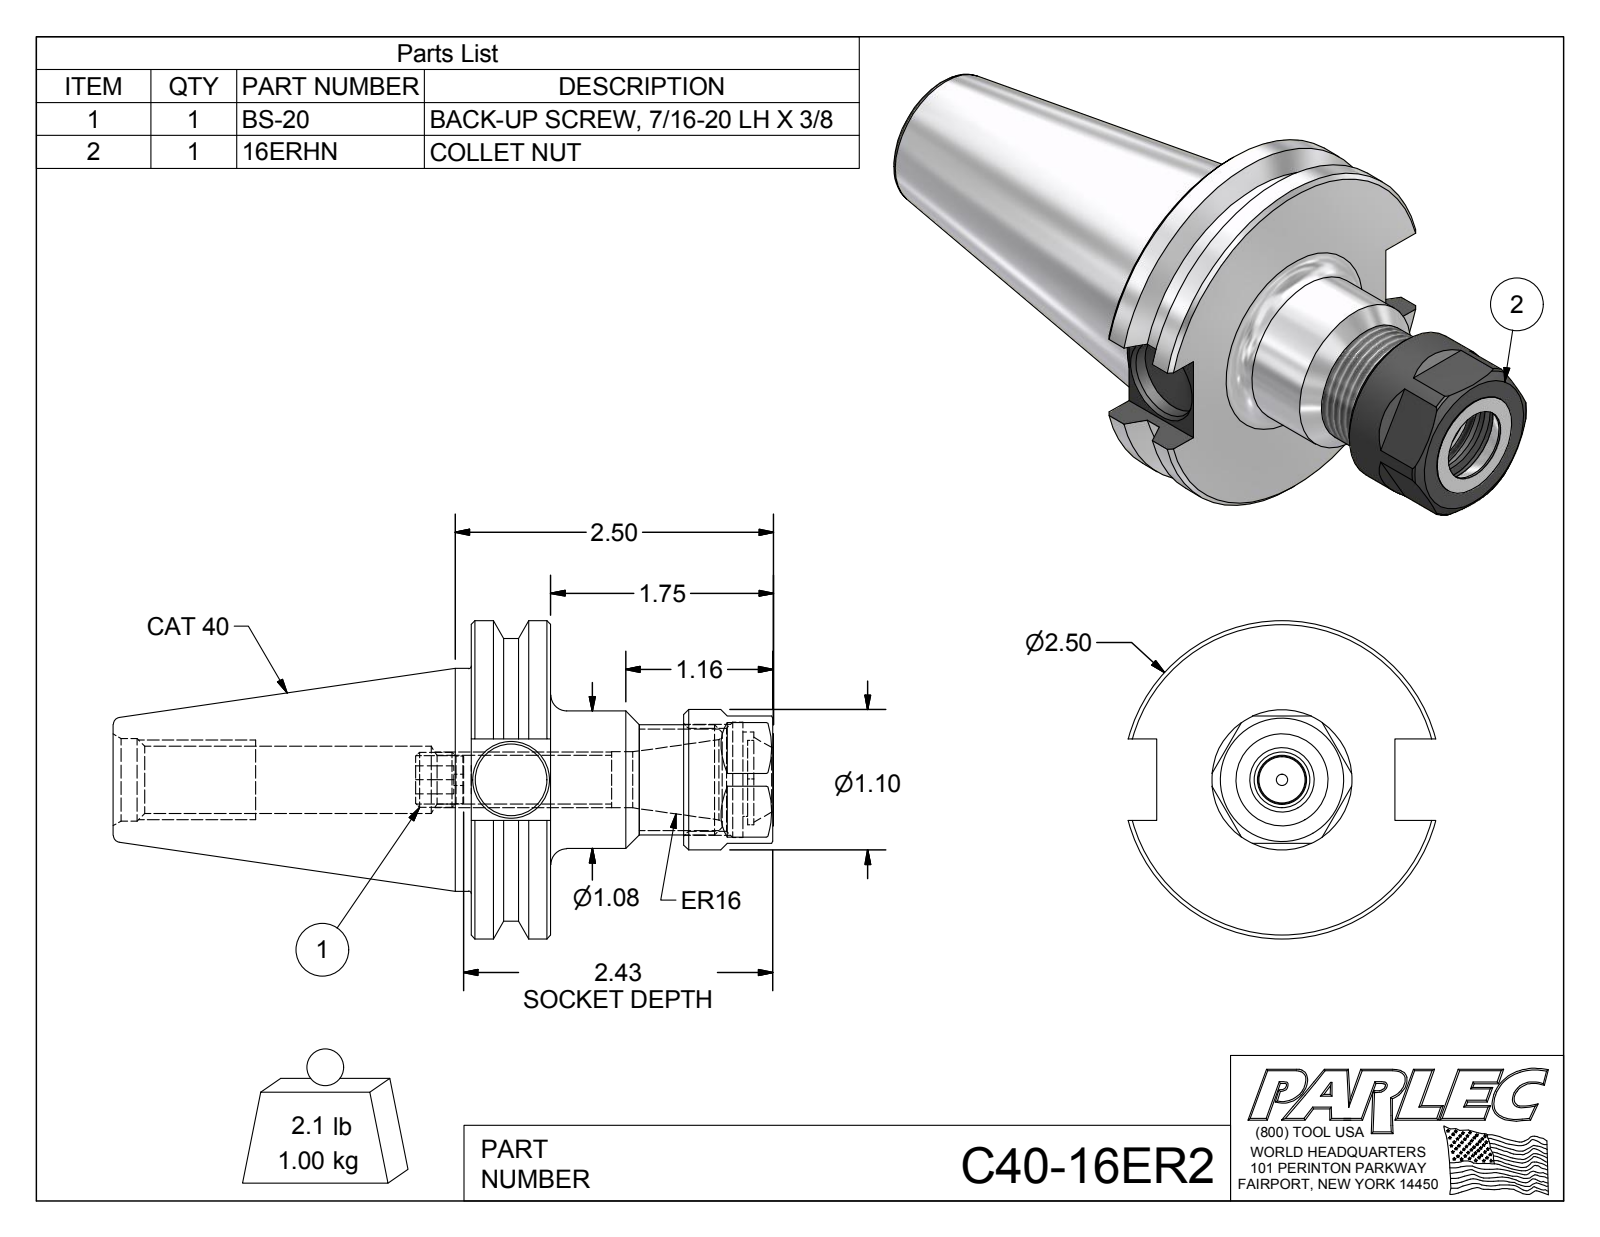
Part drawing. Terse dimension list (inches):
name: C40-16ER2; C40-16ER2-1; BS-20; 16ERHN
written by: Autodesk Inventor 2012 (AUTOMOTIVE_DESIGN)
unit: in
bodies: 3 solids, 97 faces (38 planar, 24 cylindrical, 35 other)
size: 5.188 × 2.5 × 2.417
volume: 7.339 in³; area: 42.75 in²
holes: 1× ⌀0.09, 1× ⌀0.383, 1× ⌀0.44, 1× ⌀0.508, 1× ⌀0.527, 1× ⌀0.563, 1× ⌀0.648, 1× ⌀0.661, 1× ⌀0.807, 1× ⌀0.906
bosses: 1× ⌀2.5, 1× ⌀2.219, 1× ⌀1.75, 1× ⌀1.102, 1× ⌀1.08, 1× ⌀0.866, 1× ⌀0.724, 1× ⌀0.432
rounds: 1× R0.354
face distances: 0.625, 1, 2.37, 1.745, 0.18, 0.82, 2.133, 1.509, 0.236, 0.64
hole spacings: 0.051
